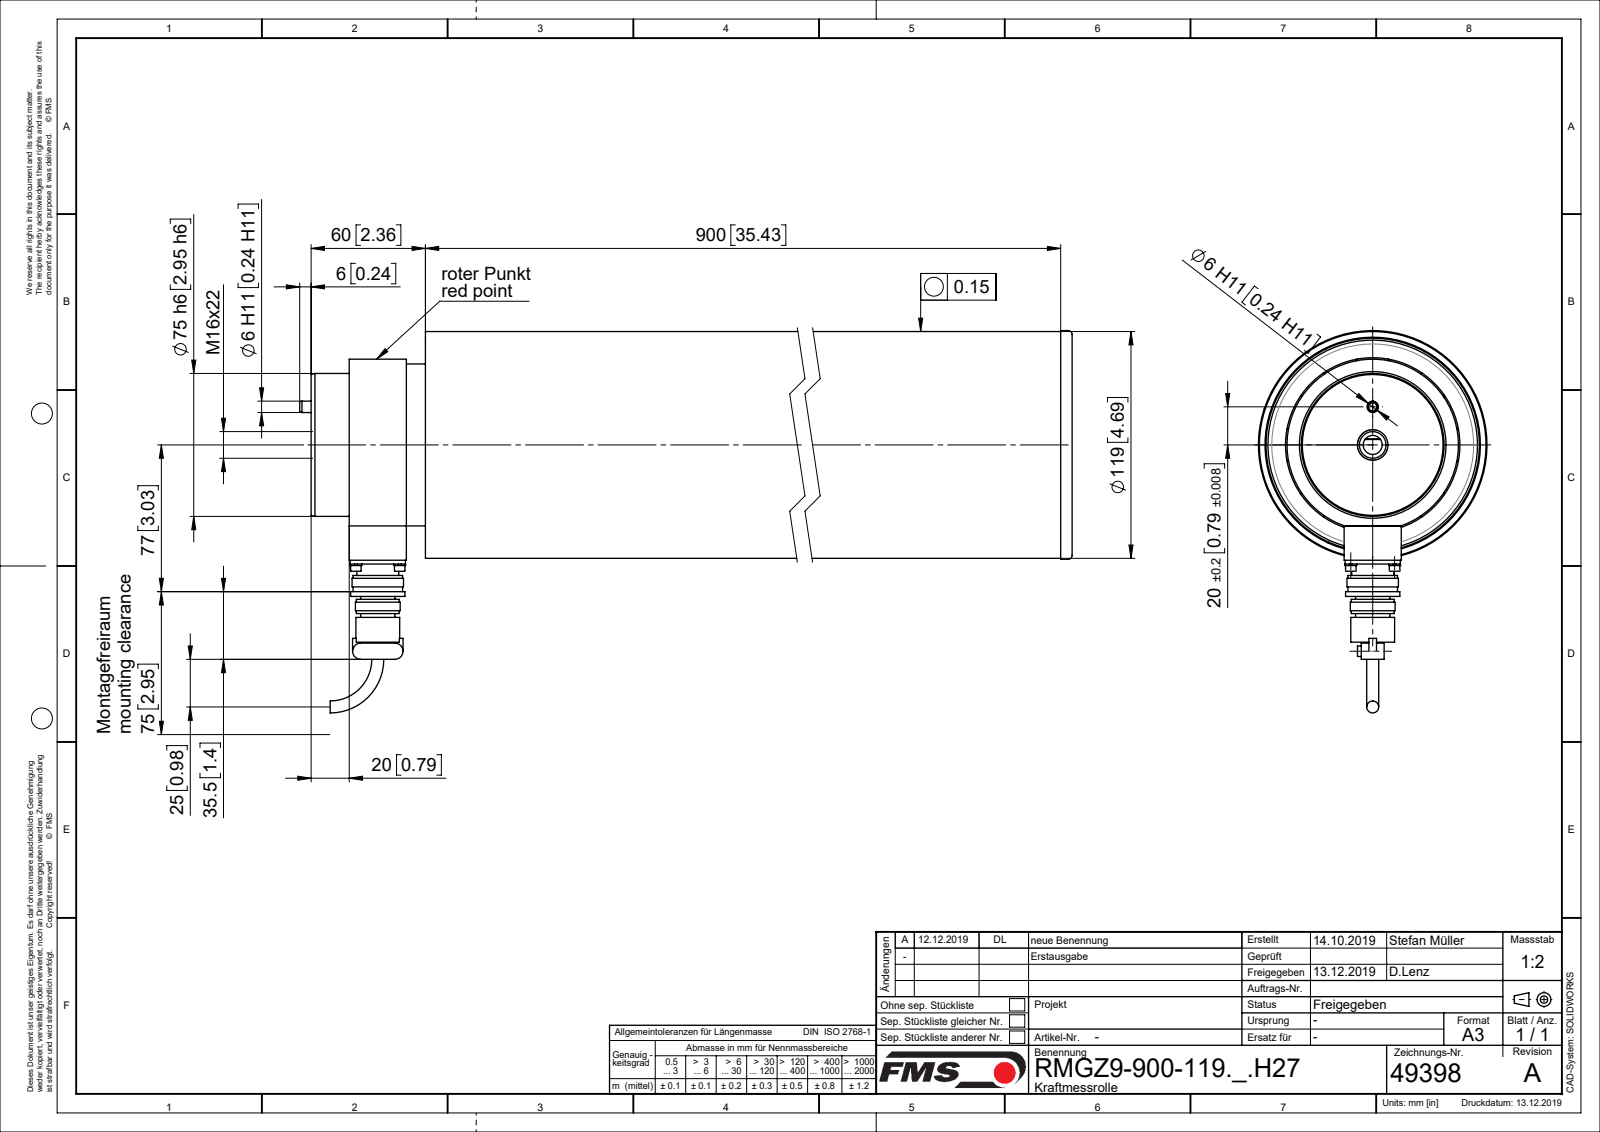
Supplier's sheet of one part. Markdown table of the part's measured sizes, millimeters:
| quantity | value |
| --- | --- |
| part name | R49398; R47848; ~TEIL1; R4768604 (+8 more) |
| STEP written by | Mechanical Desktop 2007 (CONFIG_CONTROL_DESIGN) |
| units | millimeters |
| bodies | 12 solids, 283 faces (97 planar, 140 cylindrical, 46 other) |
| overall size | 967 × 200.65 × 120 |
| volume | 3 567 000 mm³ |
| surface area | 971 350 mm² |
| round holes (diameter × count) | 2.6 × 4, 3.4 × 4, 14.21 × 1, 22 × 1, 23 × 1, 26 × 1, 40 × 1, 48.68 × 1, 50 × 1, 75 × 1, 81 × 1, 103 × 1 |
| round bosses / shafts (diameter × count) | 2.5 × 4, 5.5 × 2, 120 × 1, 119 × 1, 107 × 1, 90 × 1, 85 × 1, 68 × 1 |
| partial cylindrical surfaces (radius × count) | 4.25 × 2 |
| main face-to-face distances | 27, 149, 5, 418, 413, 176, 589, 594, 440, 445 |
| hole center spacings | 16.26, 23, 32.53 |
